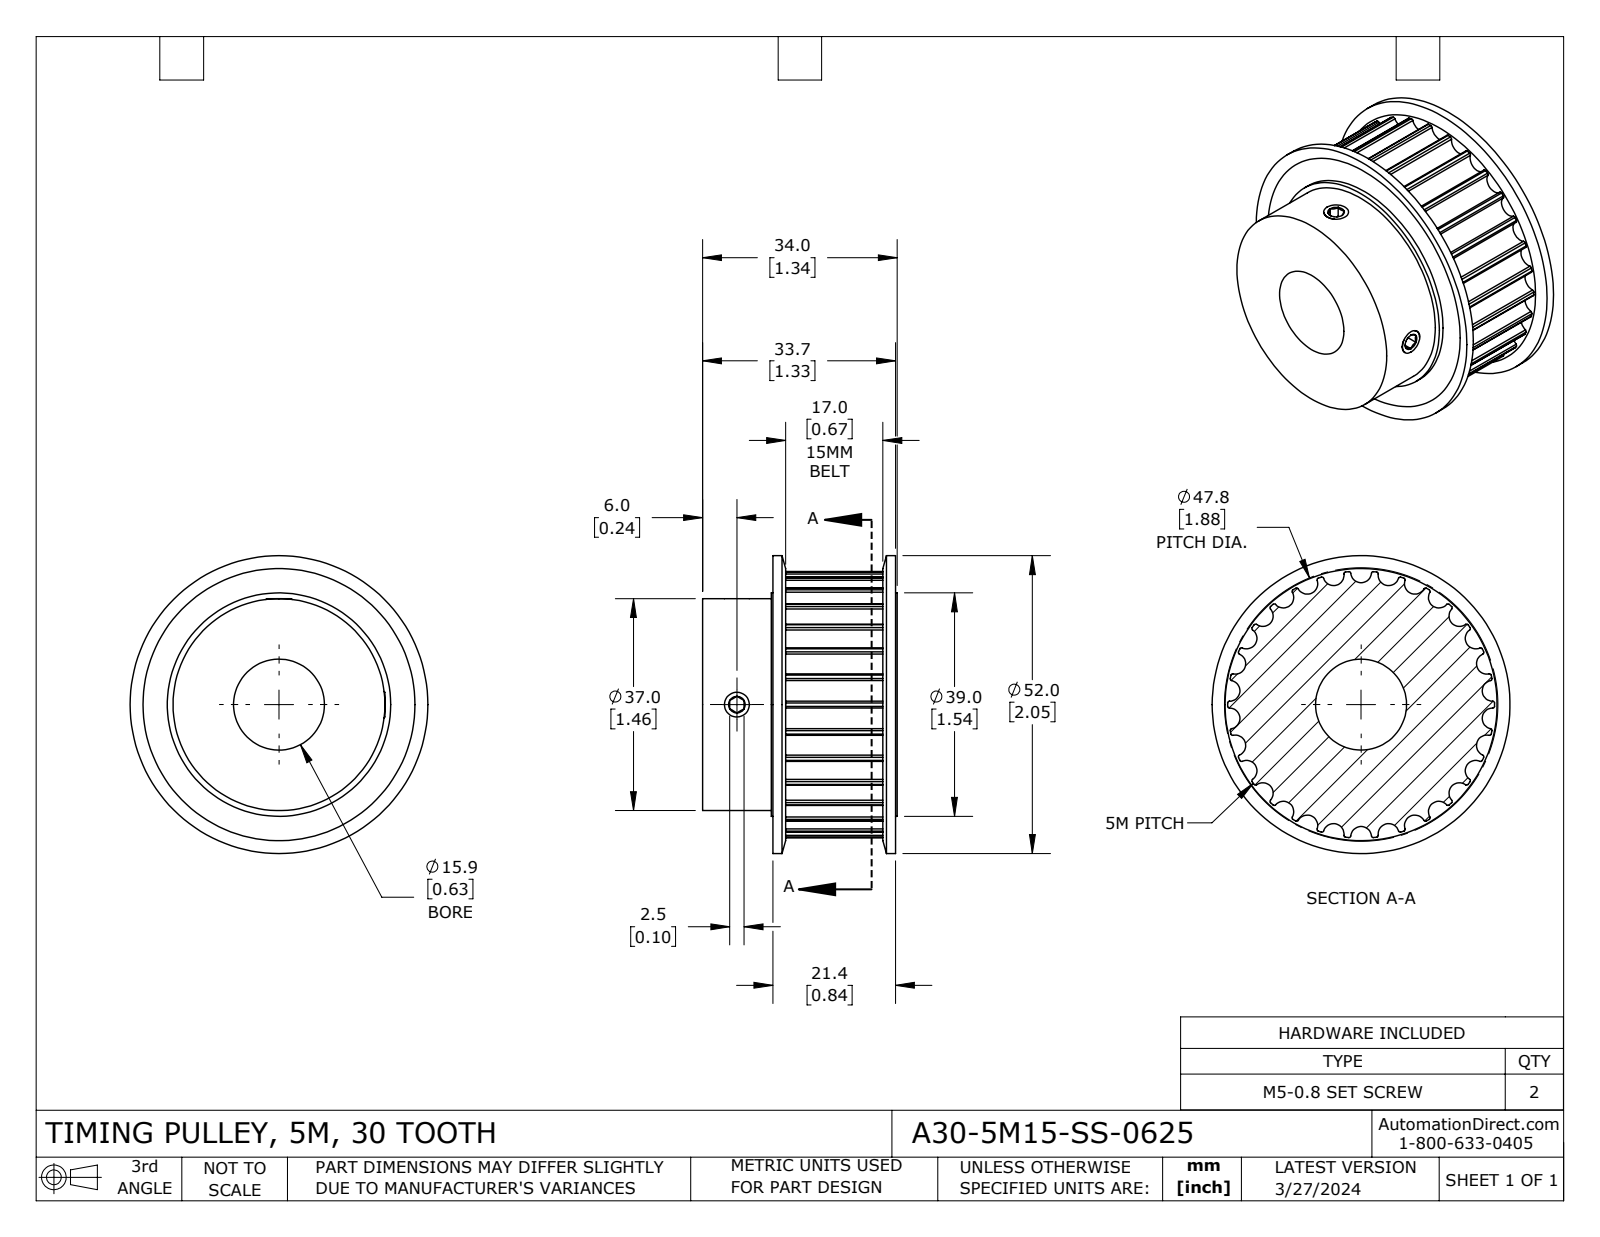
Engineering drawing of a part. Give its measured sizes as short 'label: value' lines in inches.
name: A30-5M15-SS-0625
written by: SolidWorks 2021 (CONFIG_CONTROL_DESIGN)
unit: in
bodies: 5 solids, 232 faces (25 planar, 173 cylindrical, 34 other)
size: 2.047 × 2.047 × 1.339
volume: 2.498 in³; area: 23.27 in²
holes: 2× ⌀0.165, 1× ⌀0.625, 1× ⌀1.535
bosses: 2× ⌀0.197, 1× ⌀2.047, 1× ⌀1.457
rounds: 60× R0.012, 30× R0.072, 1× R0.917
face distances: 0.063, 0.732, 0.098, 0.768, 0.669, 1.339, 1.24, 0.571, 0.035, 0.831
